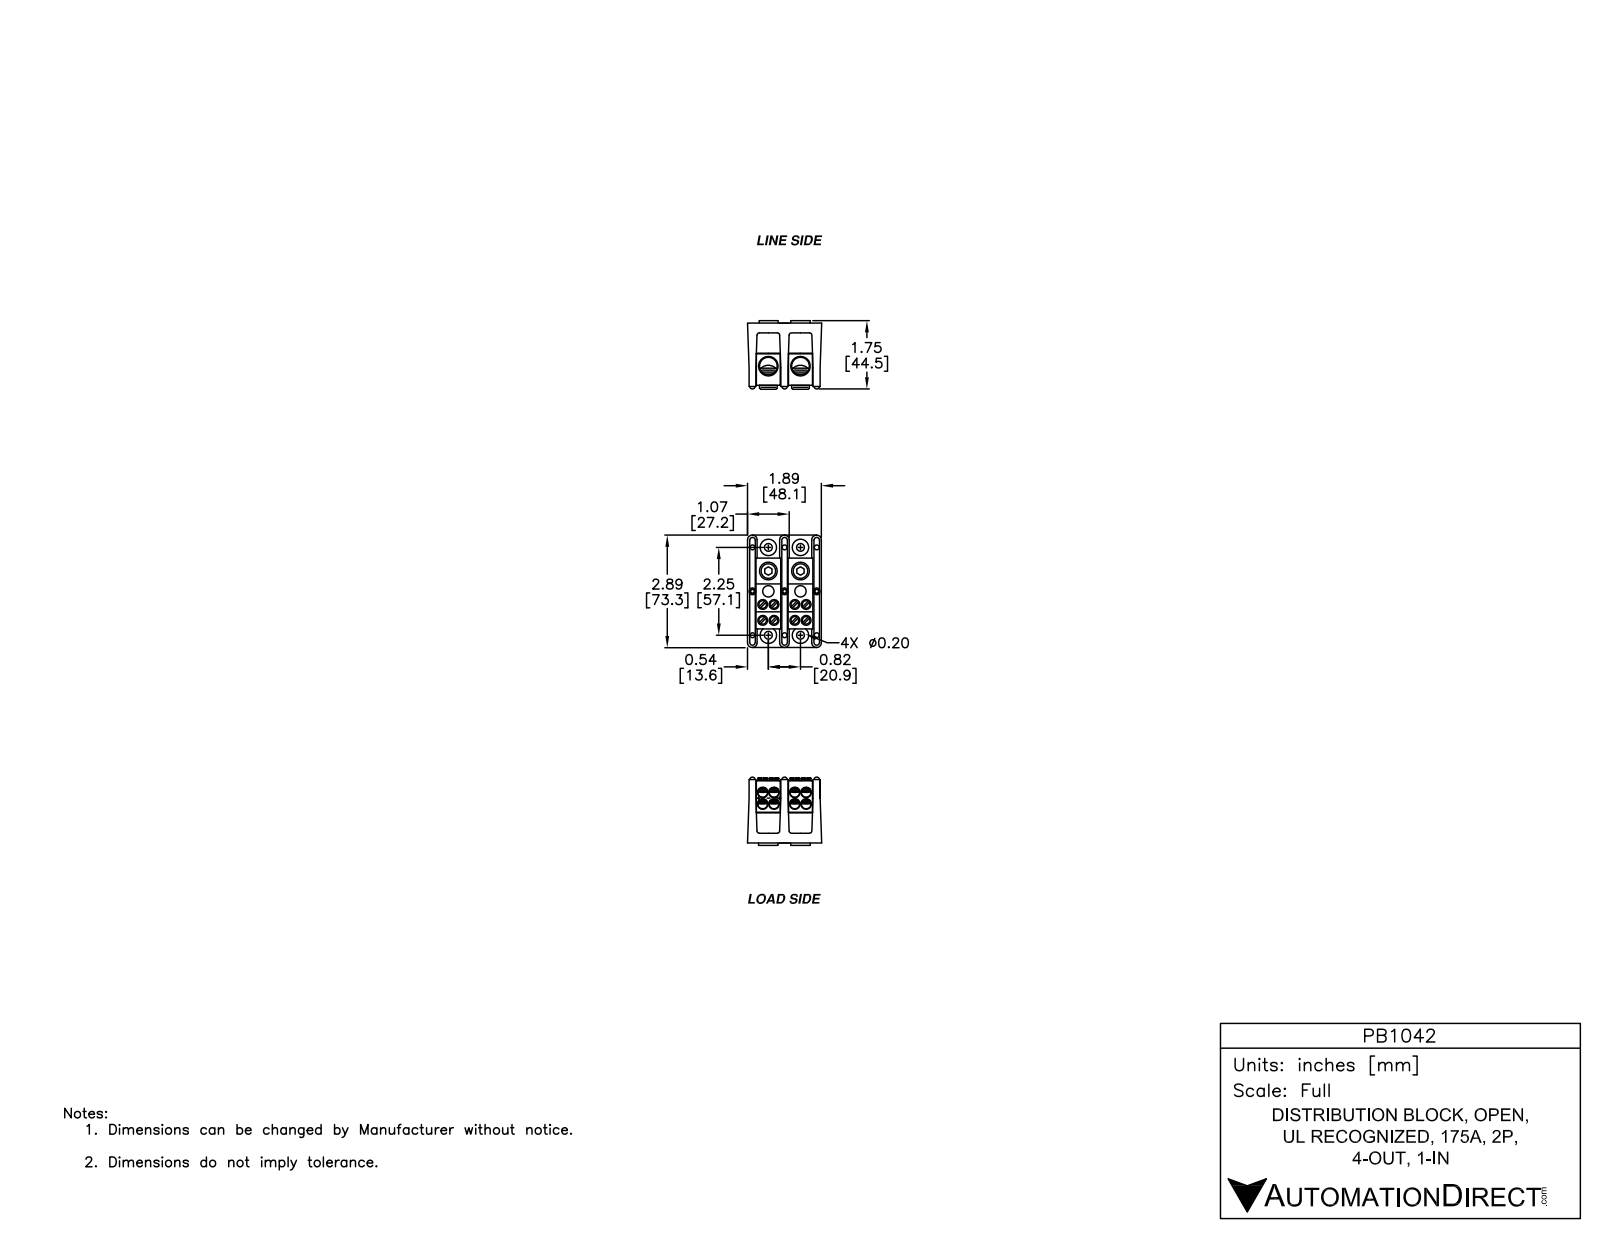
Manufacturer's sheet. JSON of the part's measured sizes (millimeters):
{"part_name": "PB1042", "step_written_by": "SolidWorks 2014 (AUTOMOTIVE_DESIGN)", "units": "millimeters", "bodies": {"solids": 15, "faces": 557, "planar": 244, "cylindrical": 219, "other": 94}, "overall_size": [72.4, 46.1, 45.9], "volume_mm3": 75940, "surface_area_mm2": 40870, "round_holes": [[5.6, 8], [6.4, 8], [5.1, 4], [2.9, 2], [4.4, 2], [5.3, 2], [7.4, 2], [10, 2], [11.5, 2], [12.7, 2], [2.9, 1]], "round_bosses_or_shafts": [[12.7, 4], [14.8, 2], [6.4, 2]], "partial_cylinders_radius": [[0.6, 43], [2.1, 3], [2.2, 2], [2.3, 2], [2.7, 2], [2.2, 1]], "face_to_face_distances": [41.5, 21, 20.6, 12.9, 6.4, 3.2, 3.2, 9.7, 16, 15.5], "hole_center_spacings": [20.8, 9.4, 20.1, 6.8, 7.9, 10.6, 11.1, 13.2]}
